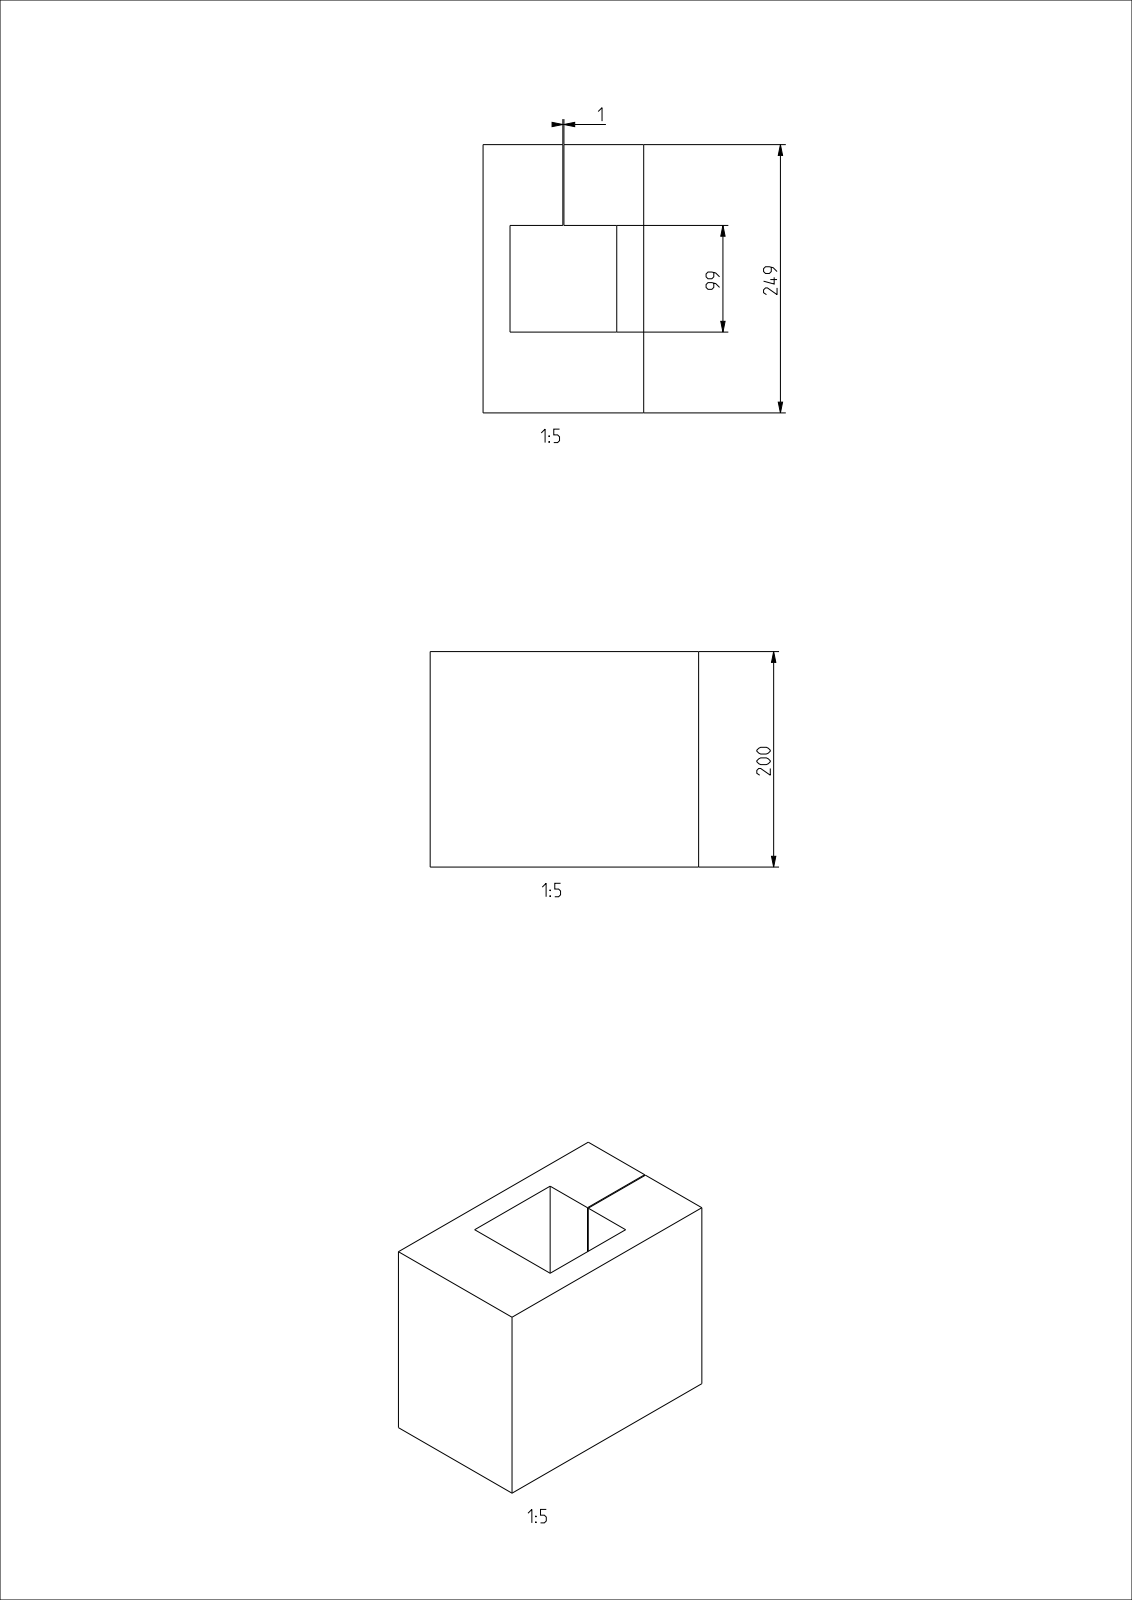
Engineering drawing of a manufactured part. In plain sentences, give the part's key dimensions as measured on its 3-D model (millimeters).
The part is named "47669-M". Its 3-D file was written by "CREO PARAMETRIC BY PTC INC, 2022281 (AUTOMOTIVE_DESIGN)". It is 1 solid with 14 faces: 14 planar, 0 cylindrical and 0 other. Overall it measures 249 by 200 by 149 millimeters. Its volume is 5 445 000 cubic millimeters and its surface area 322 450 square millimeters. The main face-to-face distances are 75, 149, 25, 124, 99, 174, 74, 49, 50, 249.
